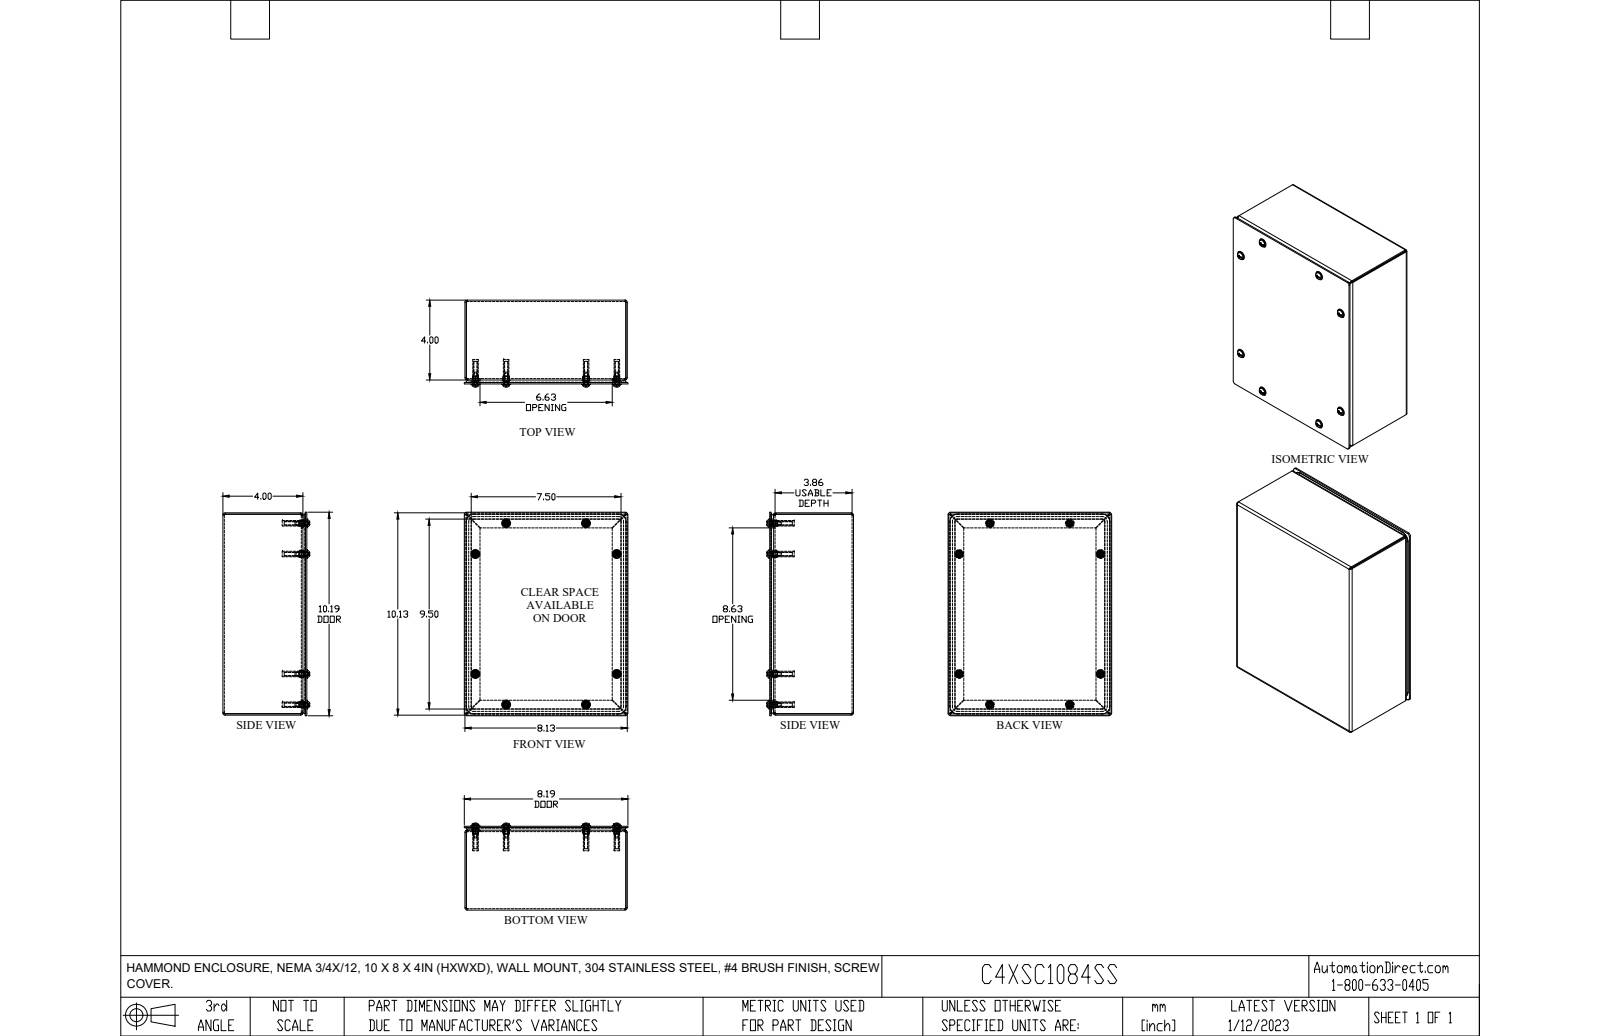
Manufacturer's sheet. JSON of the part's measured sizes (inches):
{"part_name": "C3SC1084GY", "step_written_by": "SolidWorks 2021 (AUTOMOTIVE_DESIGN)", "units": "inches", "bodies": {"solids": 27, "faces": 780, "planar": 480, "cylindrical": 152, "other": 148}, "overall_size": [10.188, 8.188, 4.347], "volume_in3": 24.45, "surface_area_in2": 723.6, "round_holes": [[0.159, 8], [0.16, 8], [0.25, 8]], "round_bosses_or_shafts": [[0.44, 8], [0.39, 8], [0.24, 8], [0.19, 8], [0.148, 8], [0.275, 4], [0.275, 4]], "partial_cylinders_radius": [[0.04, 8], [0.11, 8], [0.125, 8], [0.16, 8], [0.126, 4], [0.374, 4]], "face_to_face_distances": [0.07, 0.072, 4.127, 4.055, 4.197, 4.125, 0.07, 3.93, 8.13, 8.06], "hole_center_spacings": [2.174, 5.747, 7.693, 9.353, 4, 6, 7.075, 9.075]}
